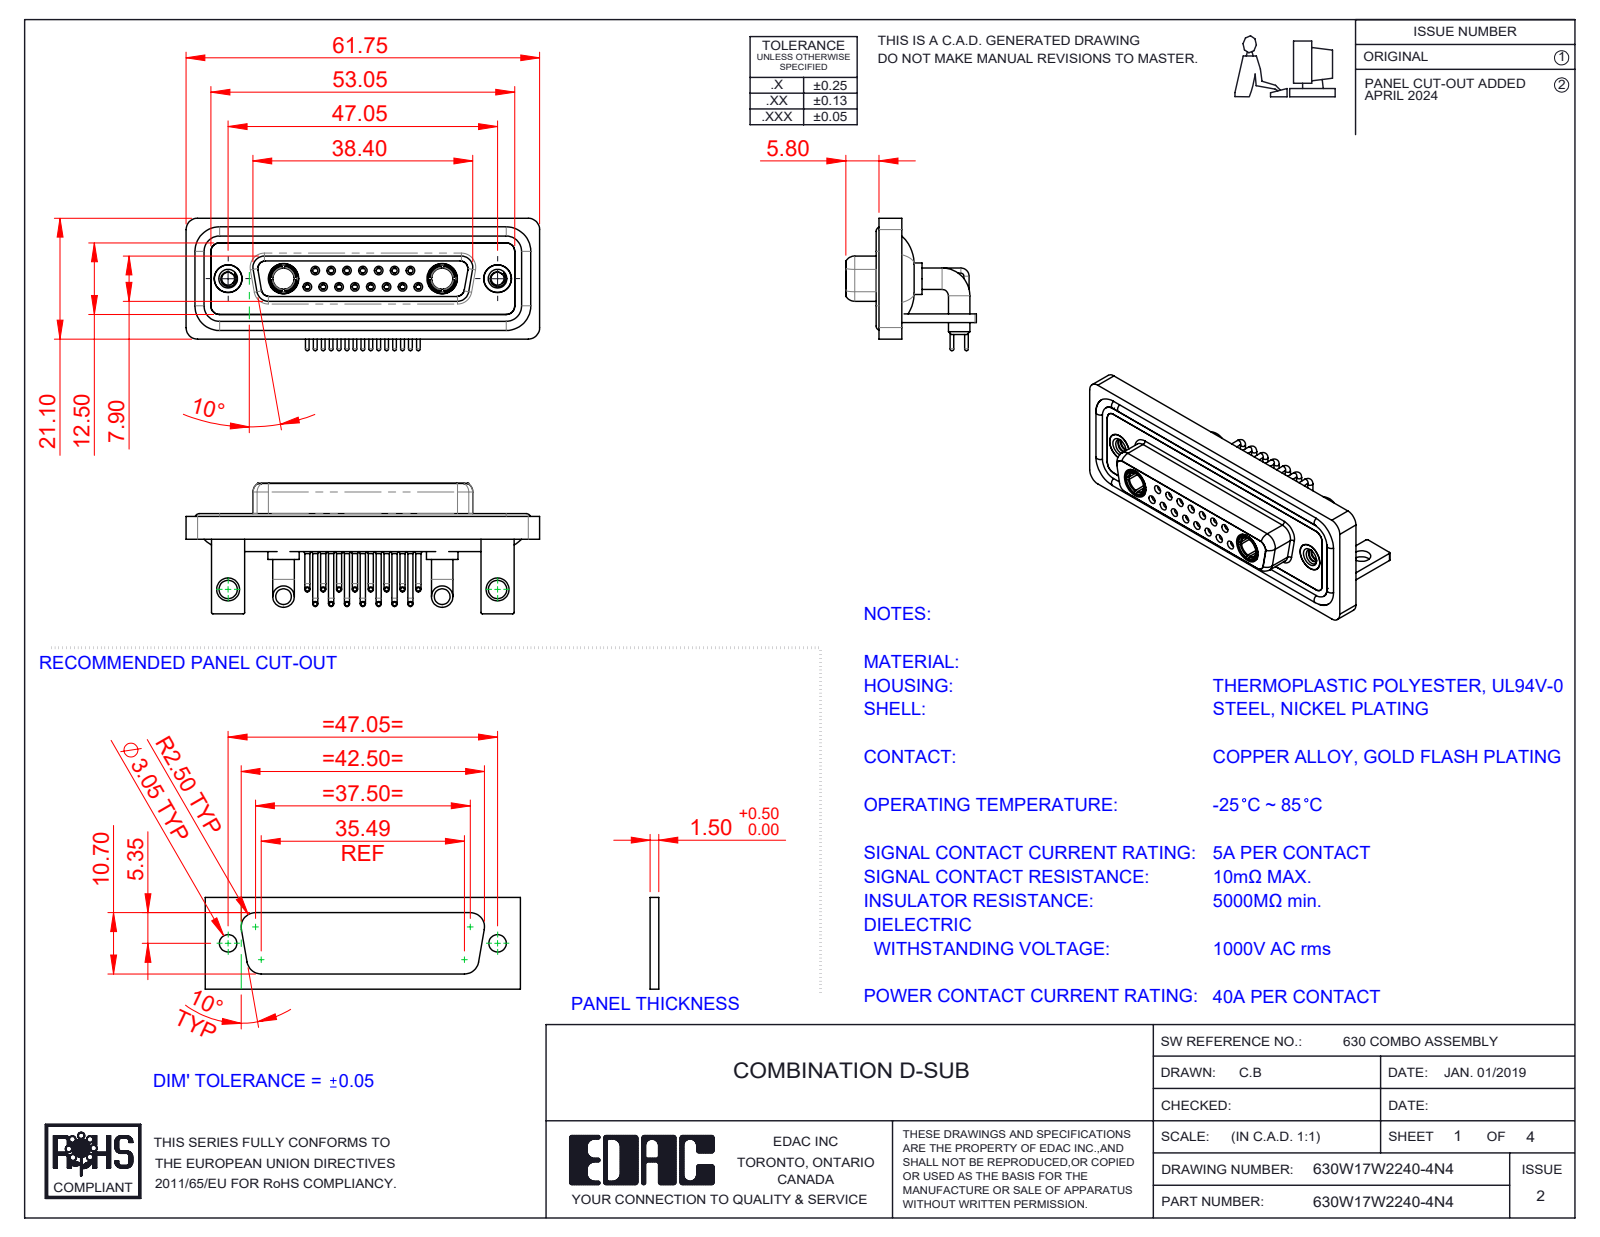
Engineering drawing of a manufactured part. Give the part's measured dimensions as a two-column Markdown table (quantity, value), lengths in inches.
| quantity | value |
| --- | --- |
| part name | 630Combo Housing_17W2; 630Combo Waterproof Housing_25 Contacts; 630Combo Contact Row 1_50 Contacts; 630Combo Shell Rear_25 Contacts (+6 more) |
| STEP written by | SolidWorks 2023 (CONFIG_CONTROL_DESIGN) |
| units | inches |
| bodies | 28 solids, 1385 faces (408 planar, 607 cylindrical, 370 other) |
| overall size | 2.431 × 0.91 × 0.898 |
| volume | 0.549 in³ |
| surface area | 23.8 in² |
| round holes (diameter × count) | 0.035 × 15, 0.043 × 15, 0.059 × 15, 0.079 × 15, 0.063 × 8, 0.067 × 7, 0.191 × 4, 0.089 × 2, 0.126 × 2, 0.146 × 2, 0.157 × 2, 0.159 × 2 |
| round bosses / shafts (diameter × count) | 0.035 × 15, 0.026 × 15, 0.063 × 11, 0.148 × 4, 0.217 × 2, 0.205 × 2, 0.195 × 2, 0.195 × 2 |
| partial cylindrical surfaces (radius × count) | 0.079 × 19, 0.059 × 18, 0.01 × 16, 0.053 × 8, 0.063 × 8, 0.02 × 5, 0.024 × 4, 0.026 × 4 |
| main face-to-face distances | 0.016, 0.071, 0.114, 0.146, 0.059, 0.161, 0.043, 0.055, 0.063, 0.122 |
| hole center spacings | 0.124, 0.109, 0.218, 0.327, 0.198, 0.295, 0.436, 0.198 |
